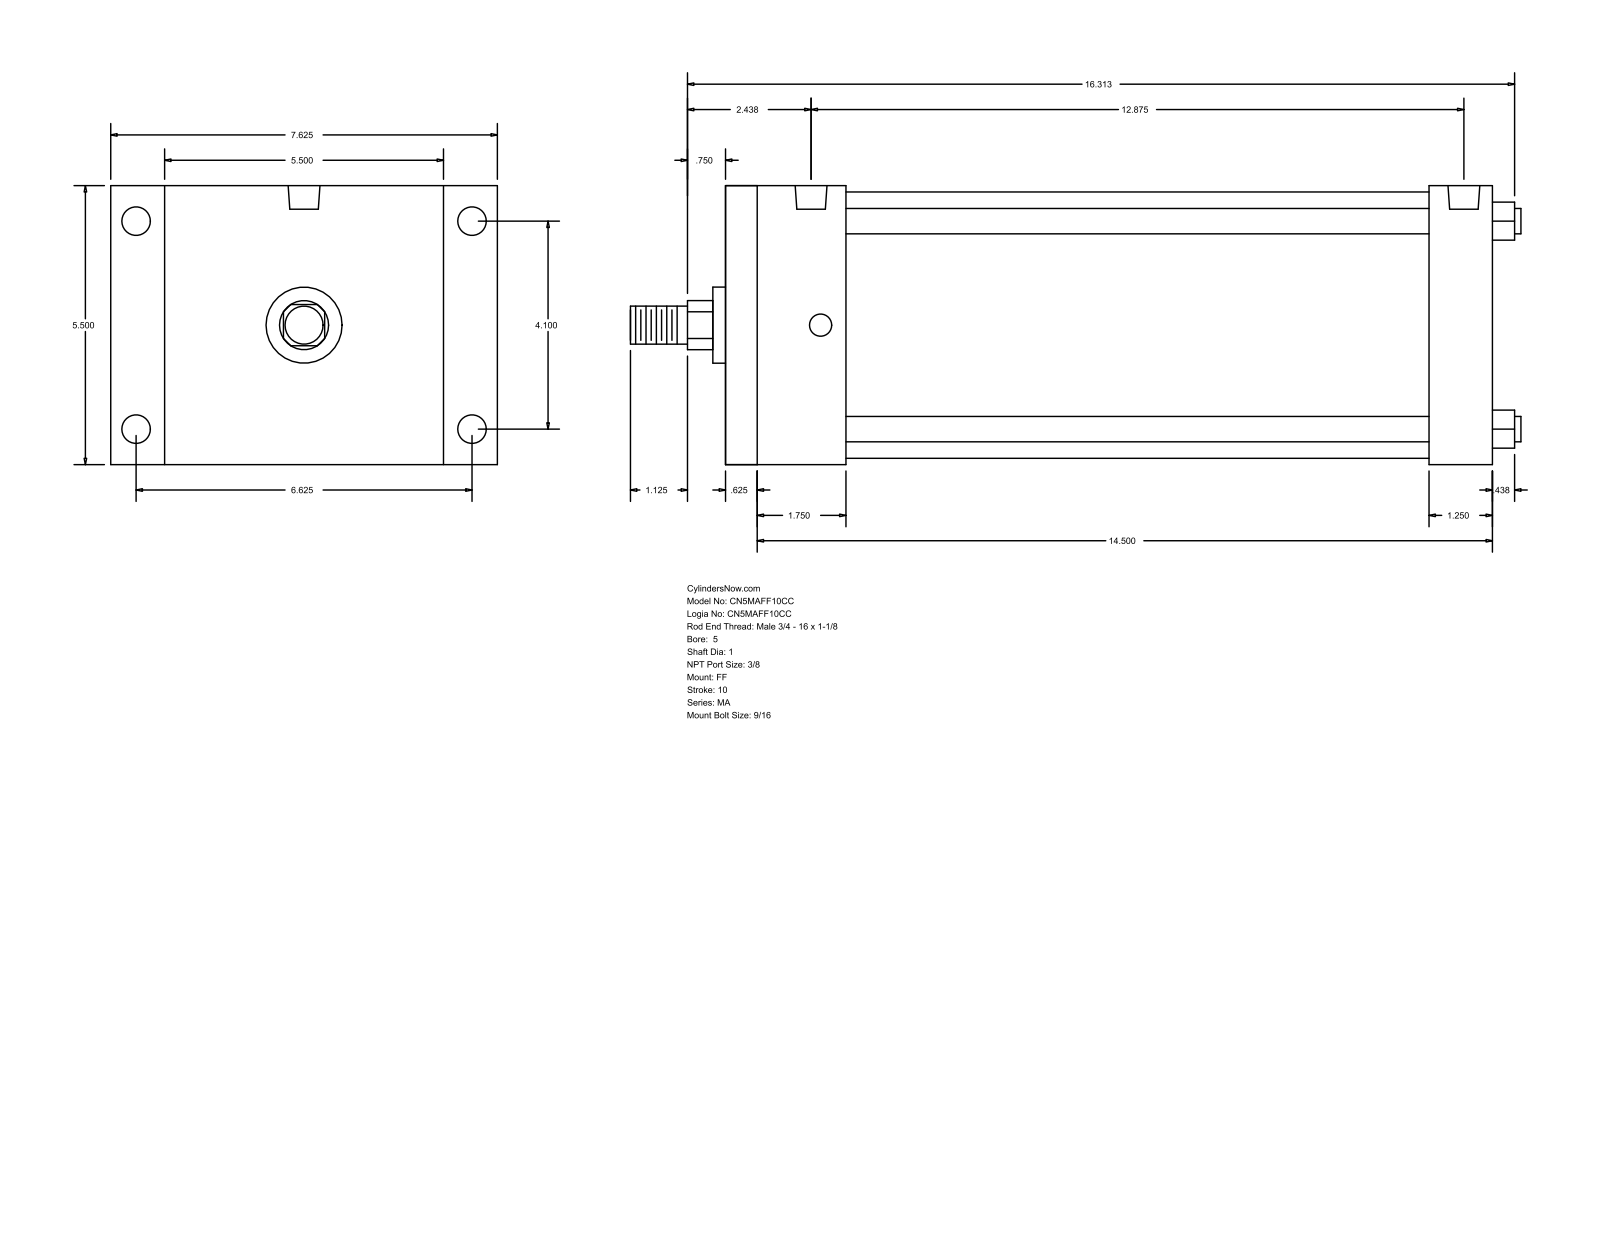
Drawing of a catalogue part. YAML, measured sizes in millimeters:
part_name: "MA_FF__0500_1"
step_written_by: "GSSL Pune (CONFIG_CONTROL_DESIGN)"
units: millimeters
bodies: {solids: 0, faces: 92, planar: 64, cylindrical: 28, other: 0}
overall_size: [446.09, 193.68, 139.7]
round_holes:
  - {diameter: 11.11, count: 4}
  - {diameter: 14.29, count: 4}
  - {diameter: 15.93, count: 2}
round_bosses_or_shafts:
  - {diameter: 12.7, count: 4}
  - {diameter: 133.35, count: 1}
  - {diameter: 38.1, count: 1}
  - {diameter: 25.4, count: 1}
  - {diameter: 19.05, count: 1}
partial_cylinders:
  - {radius: 12.29, count: 1}
face_to_face_distances: [139.7, 384.18, 15.87, 368.31, 352.43, 336.56, 31.75, 60.33, 44.46, 292.1]
hole_center_spacings: [4.76, 104.14, 168.28, 197.9, 317.51, 322.27, 327.03]
